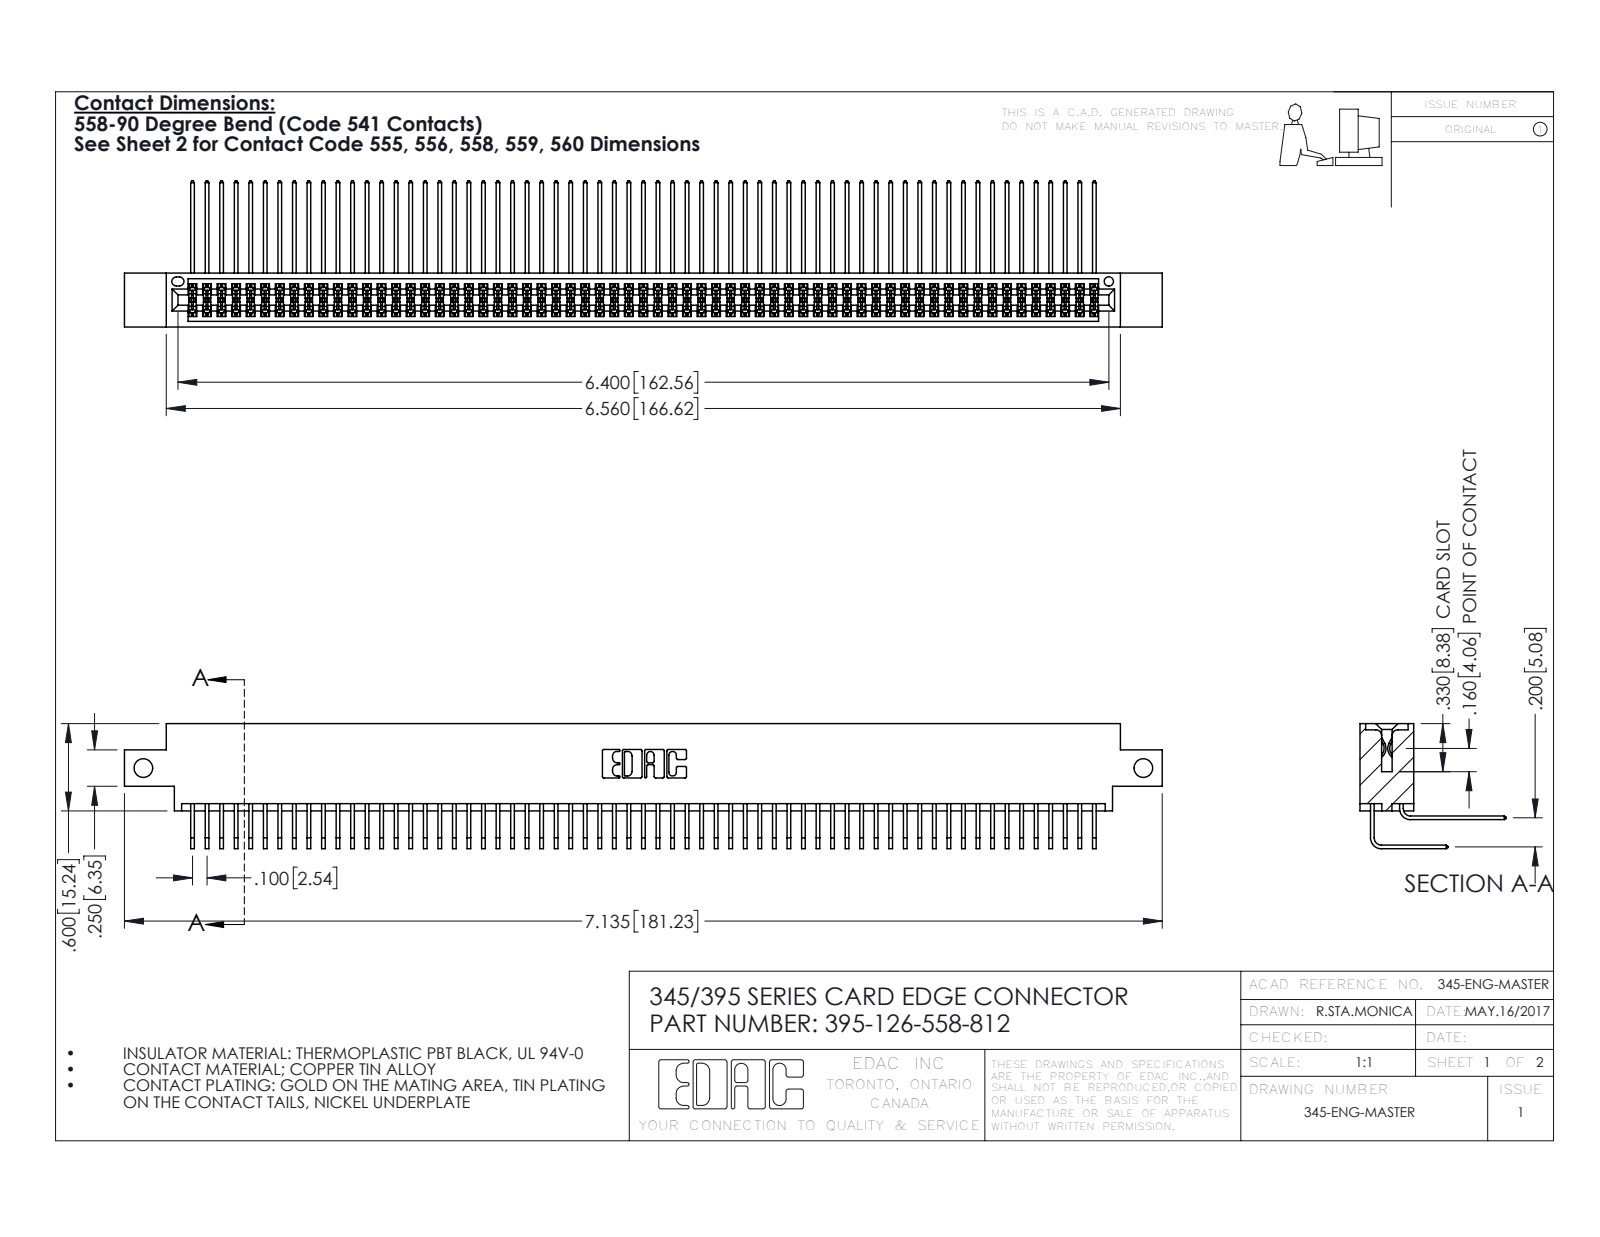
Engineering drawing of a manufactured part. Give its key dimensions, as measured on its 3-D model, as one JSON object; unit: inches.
{"part_name": "395-126-558-812; 345-292-001_558 559 Tail - 1; 345-292-001_558 Tail - 2; 345 Part_0.170 Offset - Side Mount", "step_written_by": "SolidWorks 2016 (CONFIG_CONTROL_DESIGN)", "units": "inches", "bodies": {"solids": 127, "faces": 6682, "planar": 4494, "cylindrical": 2188, "other": 0}, "overall_size": [7.135, 1.005, 0.859], "volume_in3": 1.118, "surface_area_in2": 47.93, "round_holes": [[0.128, 2], [0.064, 1]], "partial_cylinders_radius": [[0.006, 190], [0.01, 22], [0.007, 6], [0.031, 6], [0.026, 3], [0.014, 2], [0.019, 2], [0.022, 2]], "face_to_face_distances": [0.072, 0.298, 0.2, 0.37, 0.098, 0.272, 0.025, 0.225, 0.175, 0.025], "hole_center_spacings": [6.875]}
